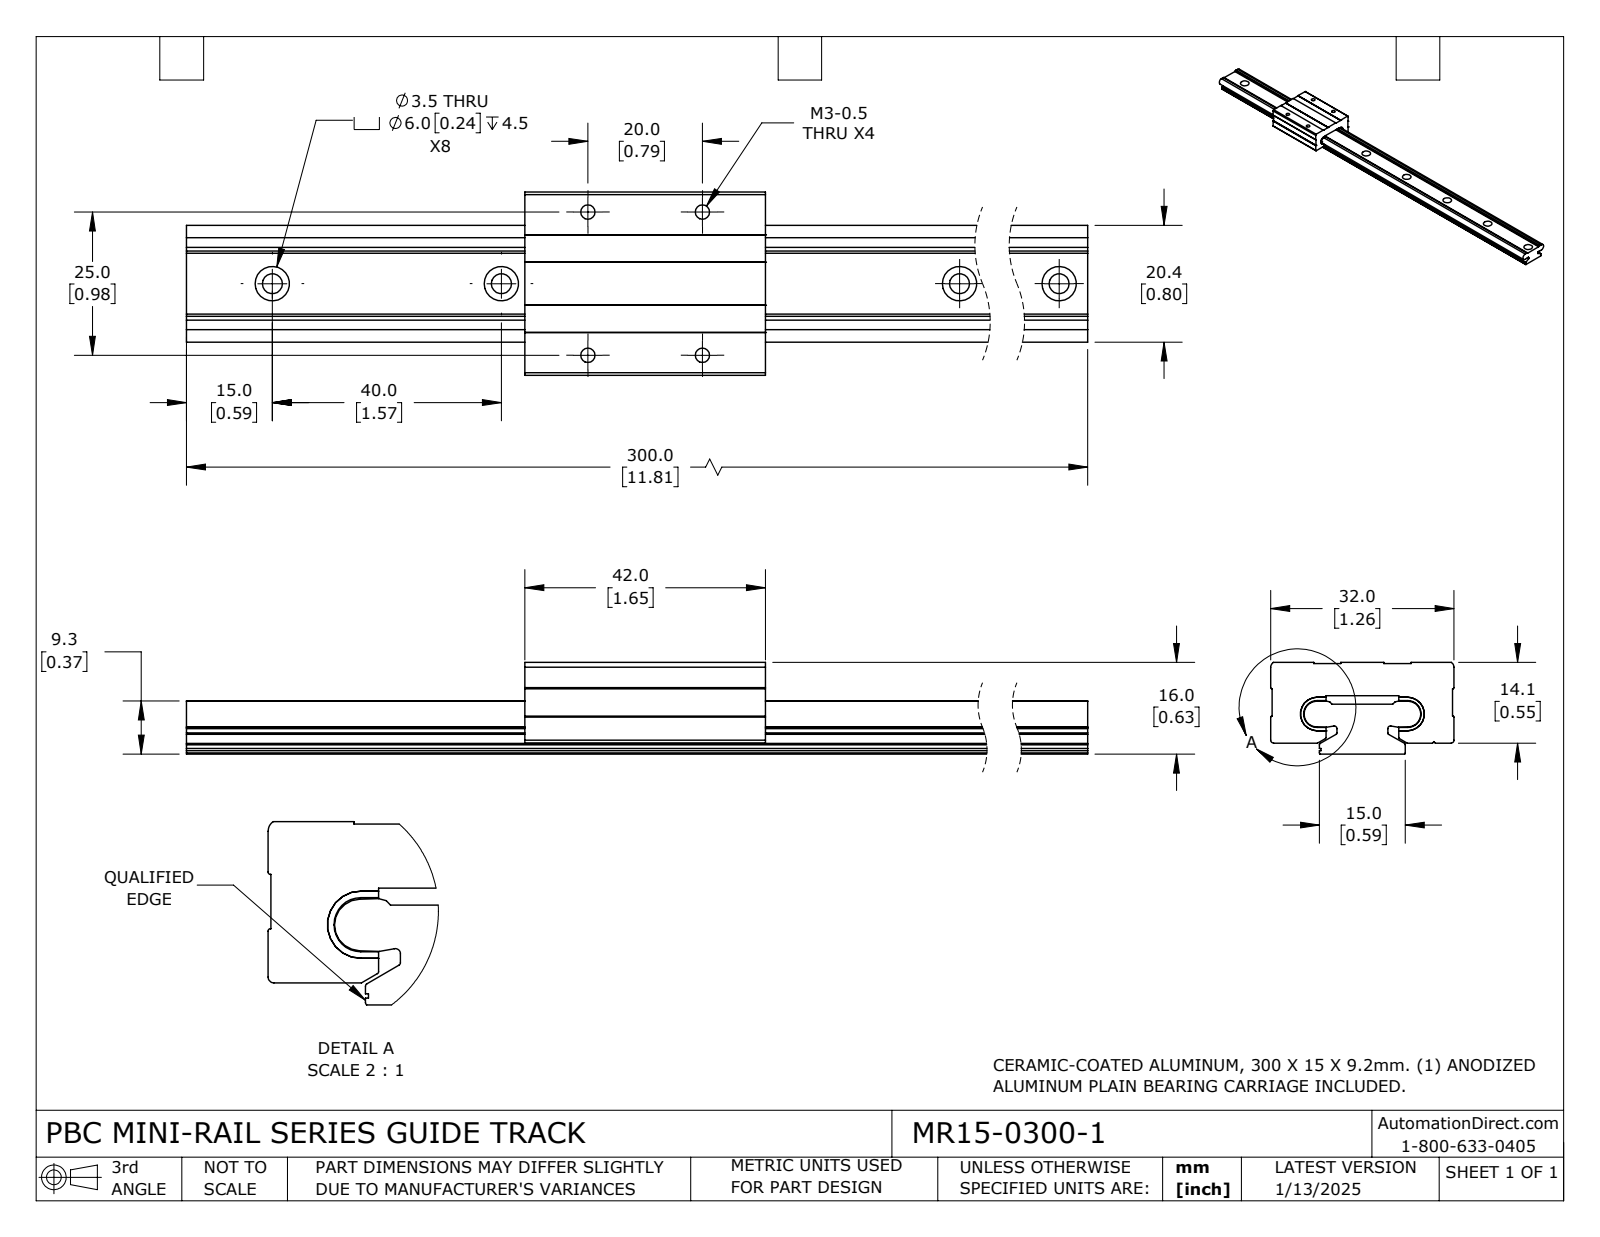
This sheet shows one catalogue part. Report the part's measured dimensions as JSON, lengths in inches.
{"part_name": "MR15-0300-1_CARRIAGE; MR15-0300-1; MR15-0300-1_RAIL", "step_written_by": "SolidWorks 2023 (CONFIG_CONTROL_DESIGN)", "units": "inches", "bodies": {"solids": 4, "faces": 168, "planar": 91, "cylindrical": 77, "other": 0}, "overall_size": [11.811, 1.26, 0.63], "volume_in3": 3.247, "surface_area_in2": 44.9, "round_holes": [[0.138, 8], [0.236, 8], [0.098, 4]], "partial_cylinders_radius": [[0.008, 12], [0.01, 6], [0.092, 4], [0.018, 2], [0.02, 2], [0.04, 2], [0.089, 2], [0.116, 2]], "face_to_face_distances": [0.343, 0.196, 0.63, 0.287, 0.335, 0.925, 0.076, 0.268, 0.554, 0.401], "hole_center_spacings": [1.575, 3.15, 4.724, 6.299, 7.874, 0.529, 0.772, 0.787]}
